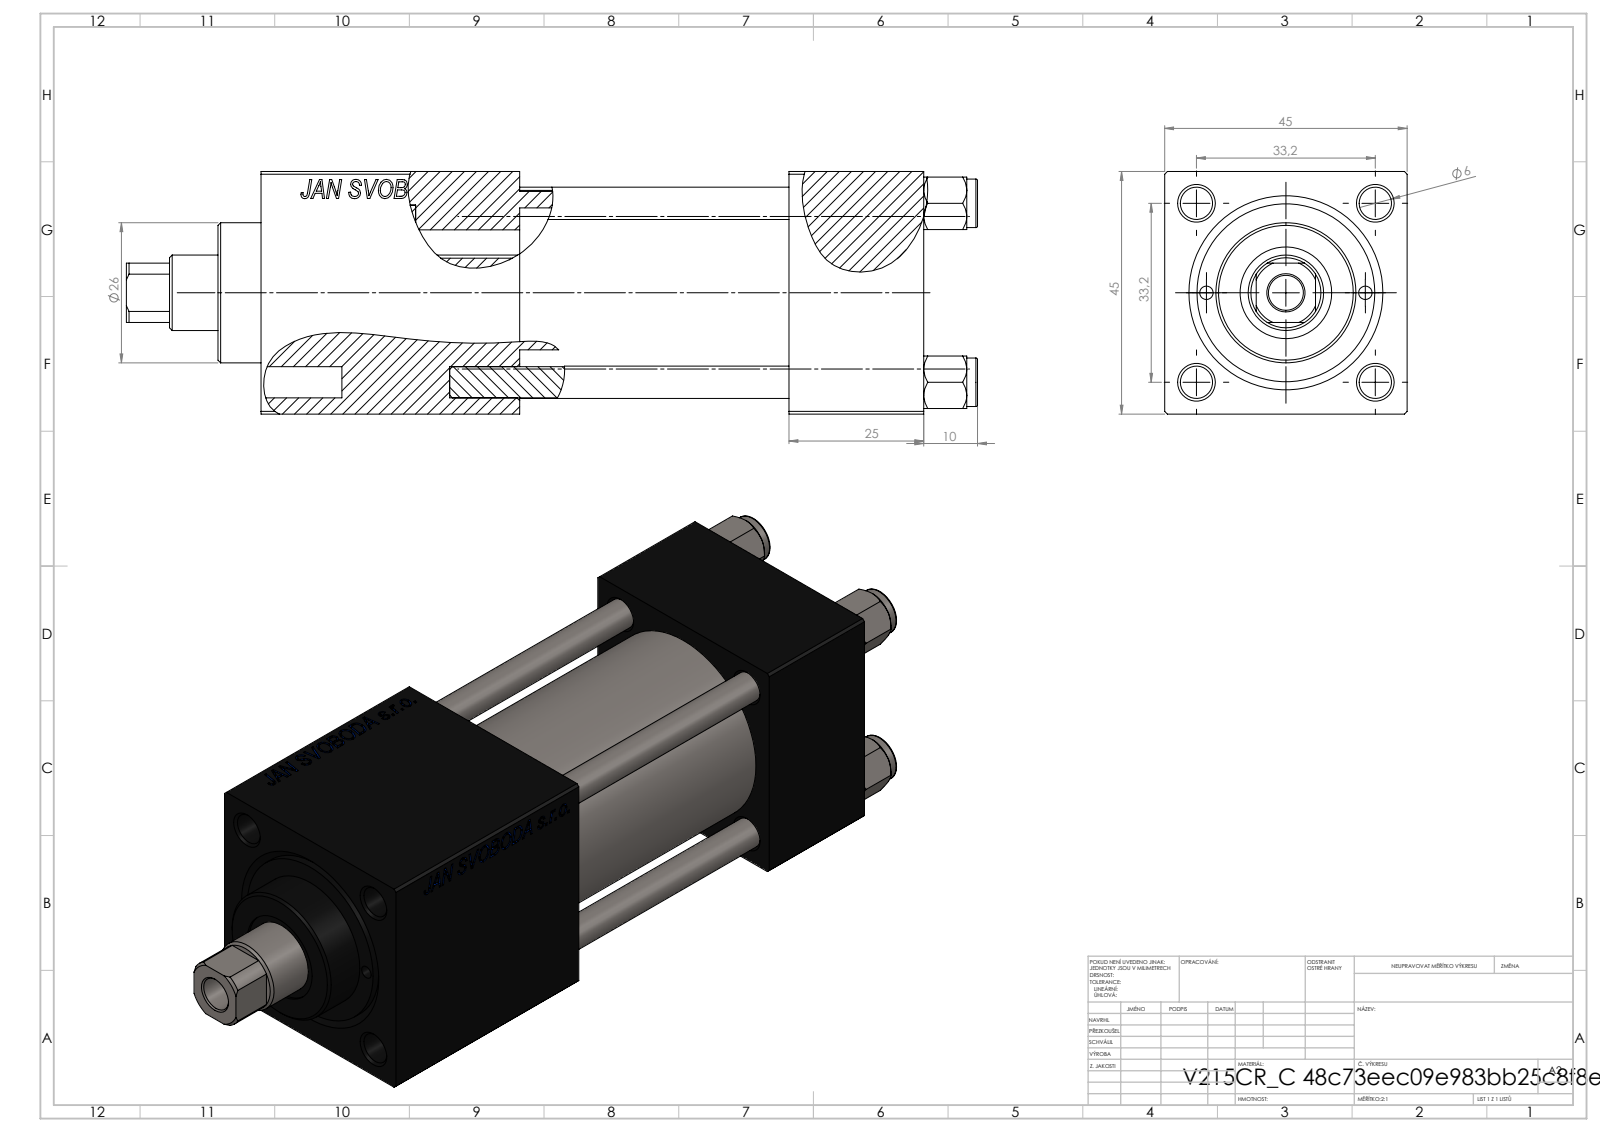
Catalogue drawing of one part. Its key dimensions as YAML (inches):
part_name: "V215CR_C_TYCINKA; V215CR_C_Body; NUT_M5_C; V215_VC_A (+1 more)"
step_written_by: "SolidWorks 2019 (CONFIG_CONTROL_DESIGN)"
units: inches
bodies: {solids: 11, faces: 1153, planar: 527, cylindrical: 90, other: 536}
overall_size: [6.22, 1.772, 1.772]
volume: 11.83
surface_area: 104.1
round_holes:
  - {diameter: 0.236, count: 4}
  - {diameter: 0.098, count: 2}
  - {diameter: 0.276, count: 2}
  - {diameter: 0.518, count: 2}
  - {diameter: 0.787, count: 2}
  - {diameter: 0.256, count: 1}
  - {diameter: 0.551, count: 1}
  - {diameter: 0.669, count: 1}
  - {diameter: 0.945, count: 1}
  - {diameter: 1.26, count: 1}
  - {diameter: 1.299, count: 1}
round_bosses_or_shafts:
  - {diameter: 0.354, count: 4}
  - {diameter: 1.496, count: 1}
  - {diameter: 1.024, count: 1}
partial_cylinders:
  - {radius: 0.256, count: 1}
face_to_face_distances: [1.772, 0.984, 3.858, 4.843, 1.969, 2.953, 1.89, 3.713, 2.728, 0.76]
hole_center_spacings: [0.657, 0.924, 1.307, 1.396, 0.581, 1.848, 1.161, 2.972]
